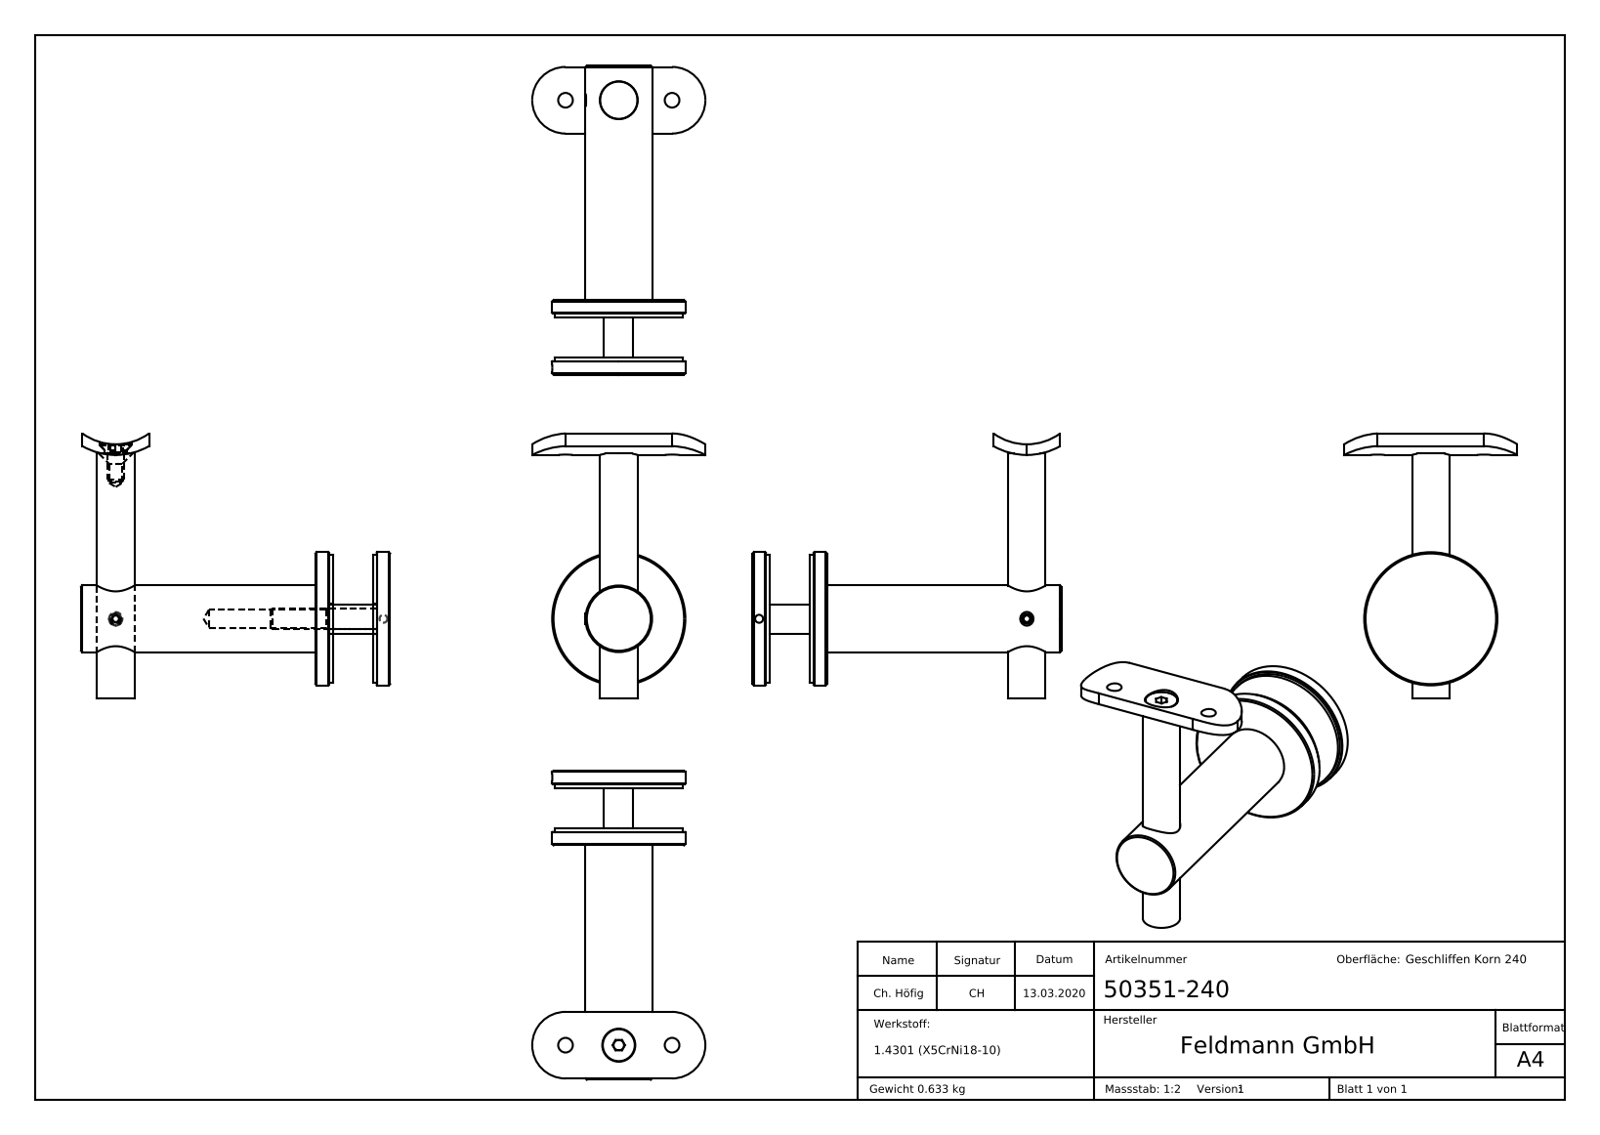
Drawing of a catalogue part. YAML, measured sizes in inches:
part_name: "503XX-240 Teil4_50351-240 Teil4; 503XX-240 Teil2_50351-240 Teil2; DIN-7991 M3-M10; 503XX-240 Teil1 (+8 more)"
step_written_by: "SolidWorks 2015 (CONFIG_CONTROL_DESIGN)"
units: inches
bodies: {solids: 9, faces: 318, planar: 166, cylindrical: 31, other: 121}
overall_size: [4.567, 3.92, 3.465]
volume: 5.199
surface_area: 56.58
round_holes:
  - {diameter: 0.217, count: 2}
  - {diameter: 0.118, count: 1}
  - {diameter: 0.165, count: 1}
  - {diameter: 0.197, count: 1}
  - {diameter: 0.268, count: 1}
  - {diameter: 0.315, count: 1}
  - {diameter: 0.319, count: 1}
  - {diameter: 0.453, count: 1}
  - {diameter: 0.488, count: 1}
  - {diameter: 0.559, count: 1}
round_bosses_or_shafts:
  - {diameter: 1.969, count: 1}
  - {diameter: 1.89, count: 1}
  - {diameter: 0.984, count: 1}
  - {diameter: 0.551, count: 1}
  - {diameter: 0.472, count: 1}
  - {diameter: 0.433, count: 1}
  - {diameter: 0.236, count: 1}
  - {diameter: 0.197, count: 1}
partial_cylinders:
  - {radius: 0.492, count: 2}
  - {radius: 0.835, count: 1}
  - {radius: 0.992, count: 1}
face_to_face_distances: [0.709, 0.059, 0.65, 0.197, 0.906, 0.256, 0.846, 0.591, 1.102, 3.72]
hole_center_spacings: [0.787, 1.575, 3.957]
